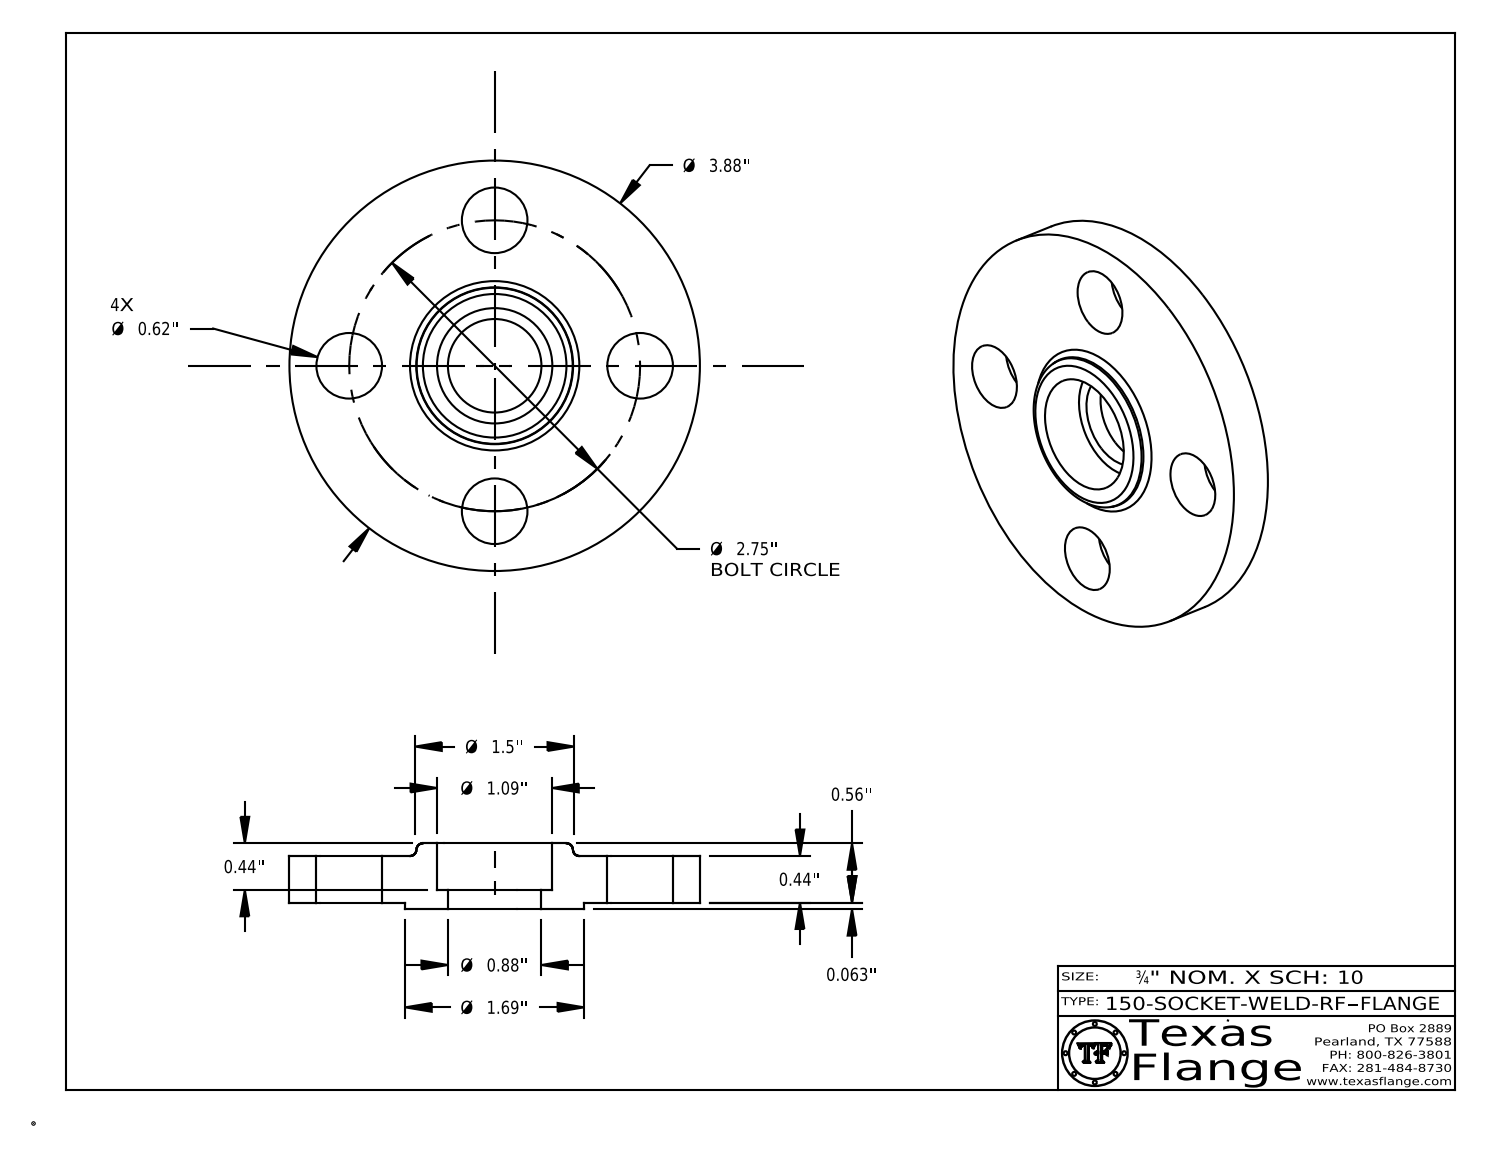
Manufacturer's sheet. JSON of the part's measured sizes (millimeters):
{"part_name": "150-SOCKET-WELD-RF", "step_written_by": "CATIA V5 STEP AP214 (AUTOMOTIVE_DESIGN)", "units": "millimeters", "bodies": {"solids": 1, "faces": 412, "planar": 370, "cylindrical": 36, "other": 6}, "overall_size": [98.6, 98.6, 15.8], "volume_mm3": 73640, "surface_area_mm2": 20350, "round_holes": [[15.7, 4], [12.6, 1], [22.5, 1], [27.7, 1]], "round_bosses_or_shafts": [[0.8, 8], [98.6, 1], [42.9, 1], [9.9, 1]], "face_to_face_distances": [11.2, 1.6, 12.8, 15.8, 14.2, 3, 4.6, 3, 8.1, 11.2], "hole_center_spacings": [34.9, 49.4, 26.7, 64.5, 69.9]}
